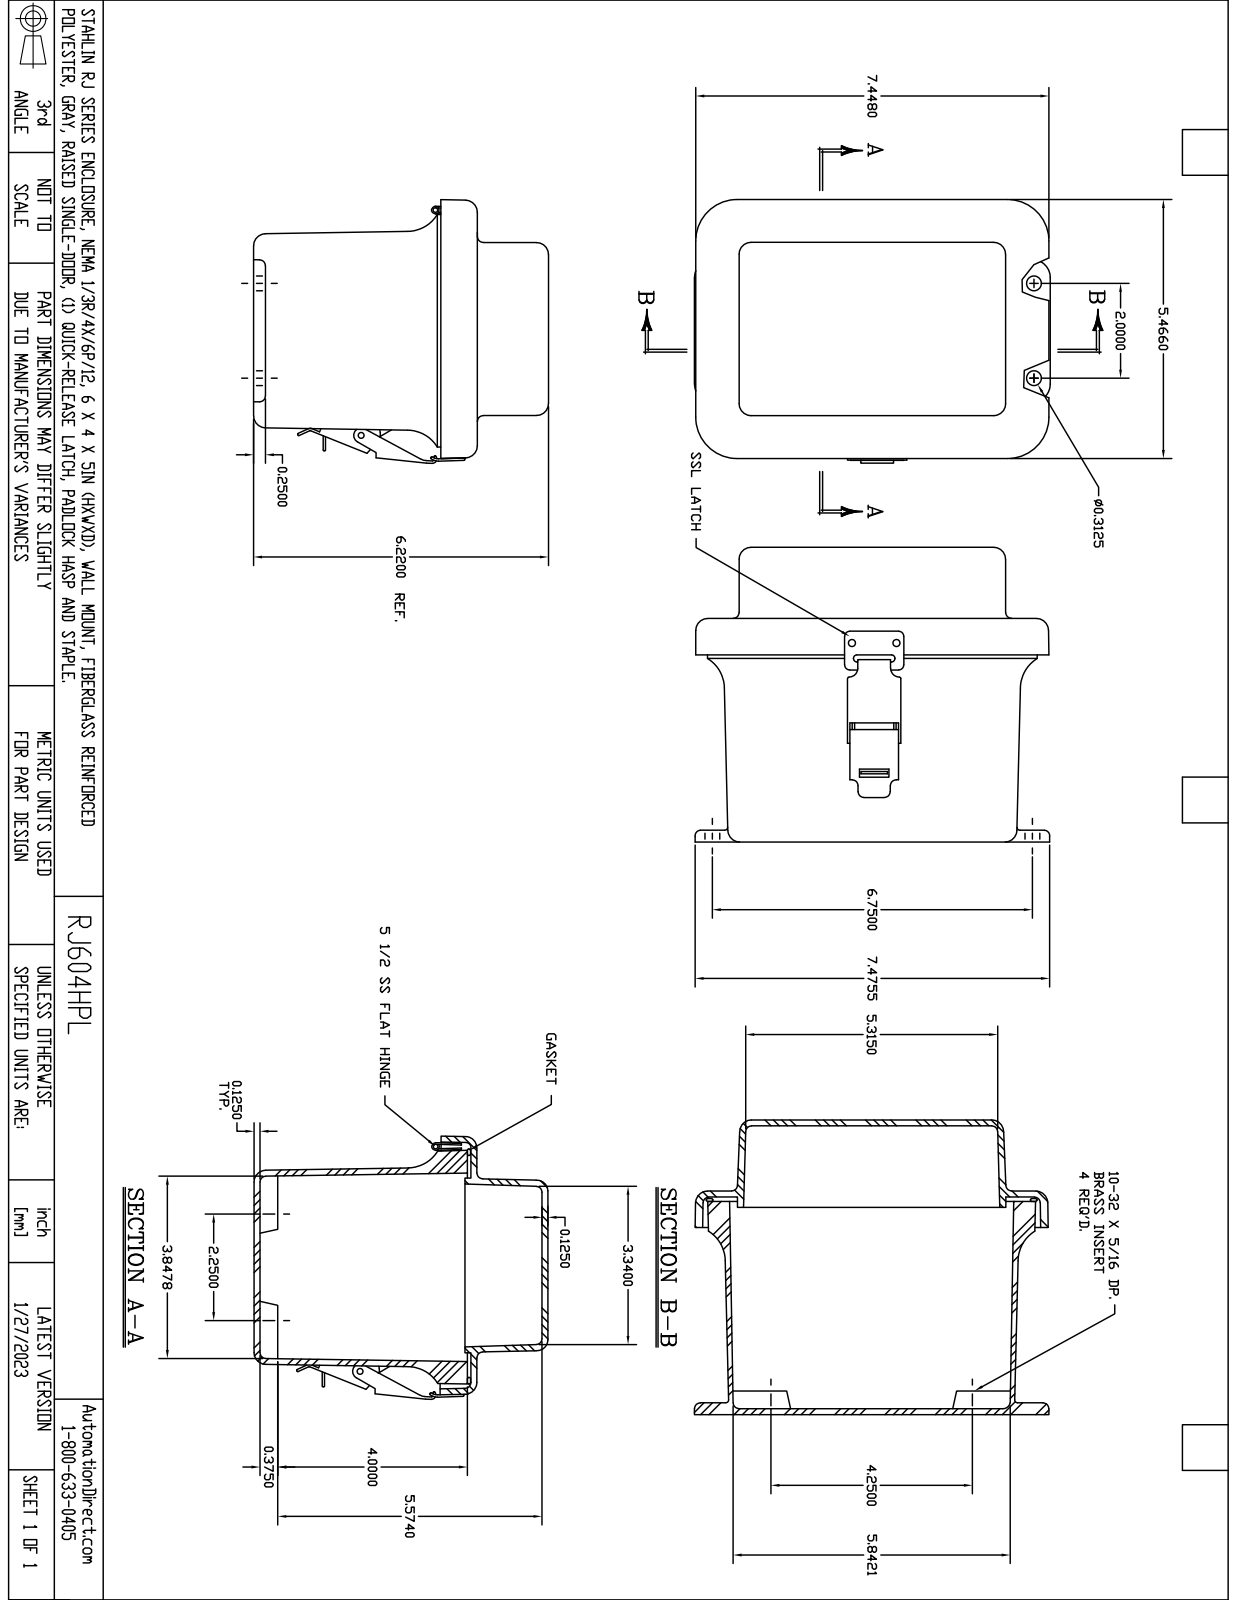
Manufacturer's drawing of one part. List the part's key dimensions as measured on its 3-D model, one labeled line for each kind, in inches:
Part name (STEP PRODUCT): MR604HPL
STEP written by: SolidWorks 2018 (AUTOMOTIVE_DESIGN)
Units: inches
Bodies: 25 solids, 694 faces (272 planar, 274 cylindrical, 148 other)
Overall size (bounding box): 7.474 × 6.227 × 5.601
Volume: 33.69 in³ · Surface area: 460.9 in²
Round holes (diameter × count): ⌀0.14 ×11, ⌀0.131 ×5, ⌀0.152 ×5, ⌀0.104 ×4, ⌀0.156 ×4, ⌀0.218 ×4, ⌀0.13 ×2, ⌀0.135 ×2, ⌀0.135 ×2, ⌀0.085 ×1, ⌀0.375 ×1
Round bosses / shafts (diameter × count): ⌀0.25 ×5, ⌀0.125 ×5, ⌀0.27 ×4, ⌀0.125 ×4, ⌀0.3 ×1, ⌀0.17 ×1, ⌀0.155 ×1, ⌀0.155 ×1
Partial cylindrical surfaces — rounded edges, fillets, slot ends (radius × count): R0.125 ×24, R0.031 ×20, R0.015 ×12, R0.25 ×12, R0.045 ×8, R0.03 ×6, R0.022 ×4, R0.06 ×4
Main face-to-face distances: 0.125, 4.602, 6.102, 1.5, 6.227, 1.625, 4.477, 5.977, 0.774, 4.727
Hole centre spacings: 0.937, 2.5, 3.339, 0.75, 0.469, 0.5, 1.341, 1.467
